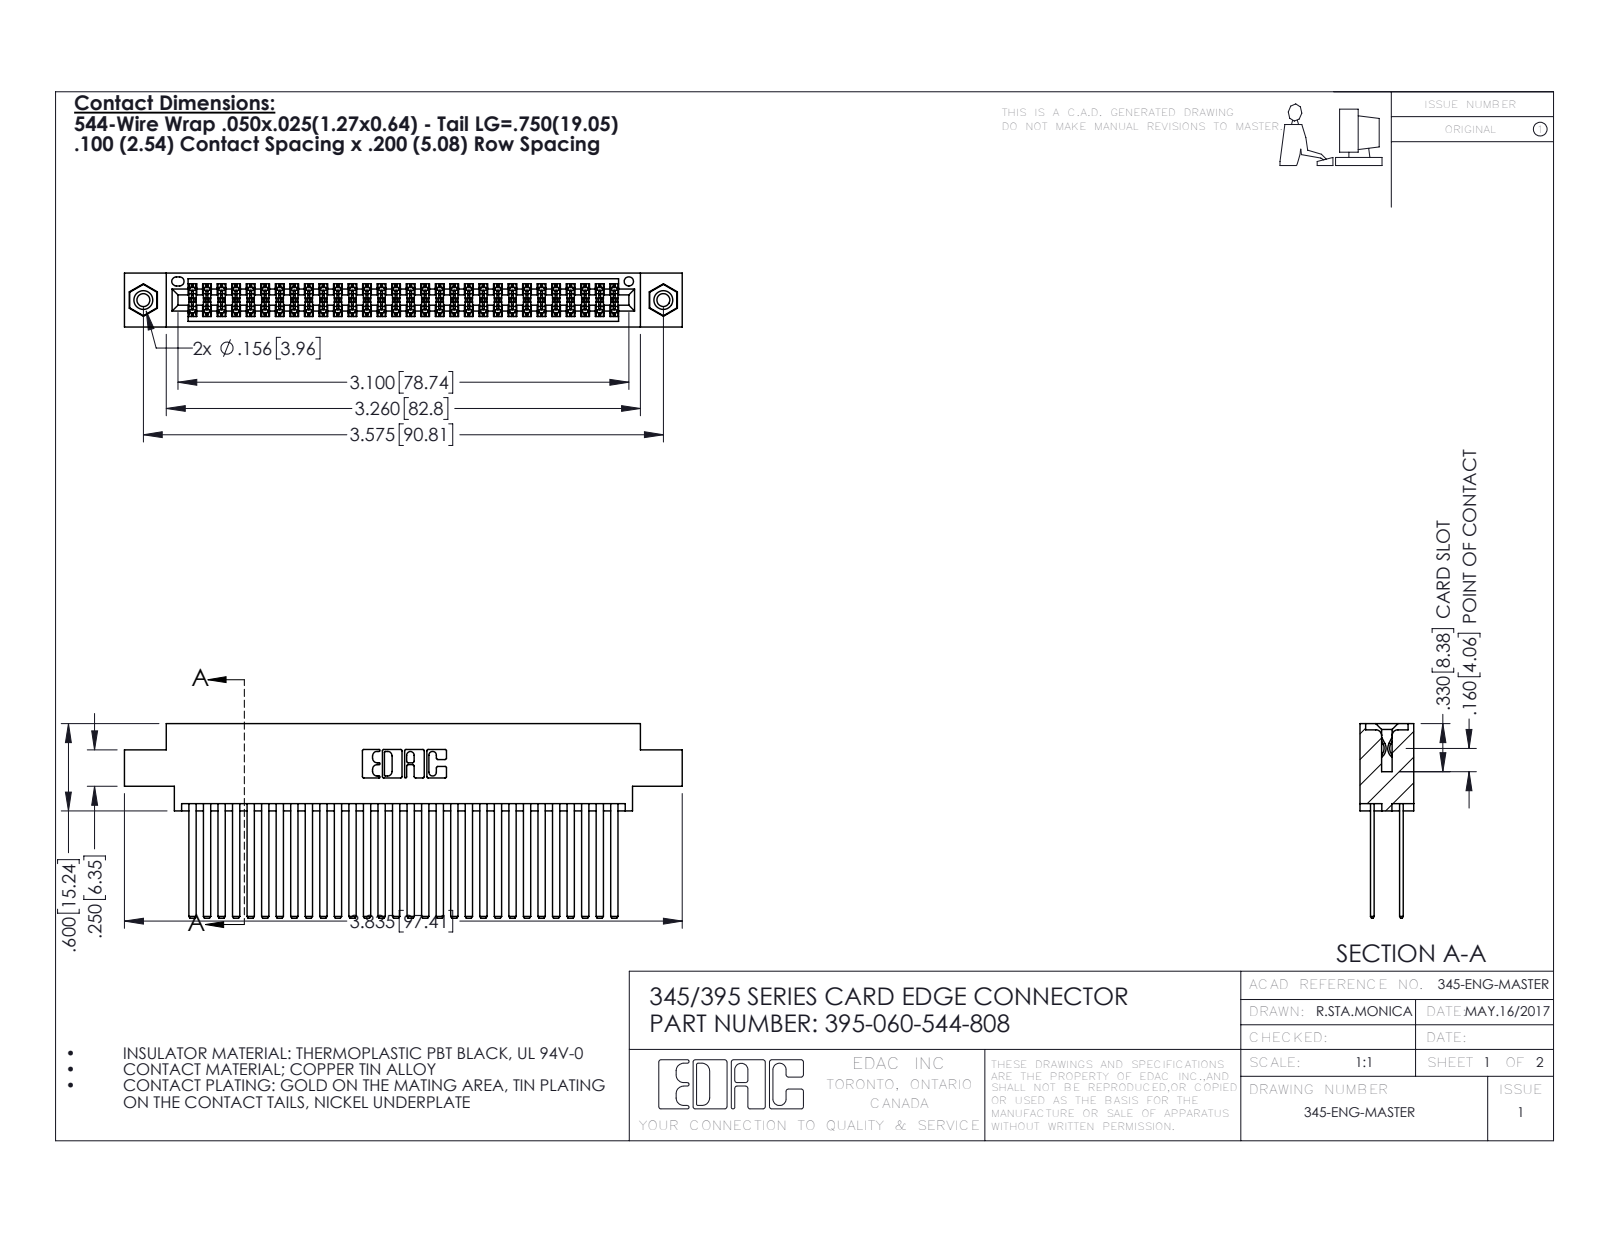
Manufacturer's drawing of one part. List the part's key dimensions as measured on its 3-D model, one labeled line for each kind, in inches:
Part name (STEP PRODUCT): 395-060-544-808; 345-292-001_345-293-144; 345-250-001_345-250-003-102; 345 Part_0.170 Offset - 0.156 Dia-TI
STEP written by: SolidWorks 2016 (CONFIG_CONTROL_DESIGN)
Units: inches
Bodies: 63 solids, 2830 faces (1856 planar, 958 cylindrical, 16 other)
Overall size (bounding box): 3.835 × 1.337 × 0.37
Volume: 0.615 in³ · Surface area: 26.78 in²
Round holes (diameter × count): ⌀0.089 ×2, ⌀0.125 ×2, ⌀0.156 ×2, ⌀0.064 ×1
Round bosses / shafts (diameter × count): ⌀0.155 ×2
Partial cylindrical surfaces — rounded edges, fillets, slot ends (radius × count): R0.006 ×90, R0.01 ×22, R0.007 ×6, R0.031 ×6, R0.026 ×3, R0.014 ×2, R0.019 ×2, R0.022 ×2
Main face-to-face distances: 0.2, 0.025, 0.072, 0.098, 0.272, 0.298, 0.225, 0.175, 0.37, 0.15
Hole centre spacings: 0.27, 3.34, 3.575
